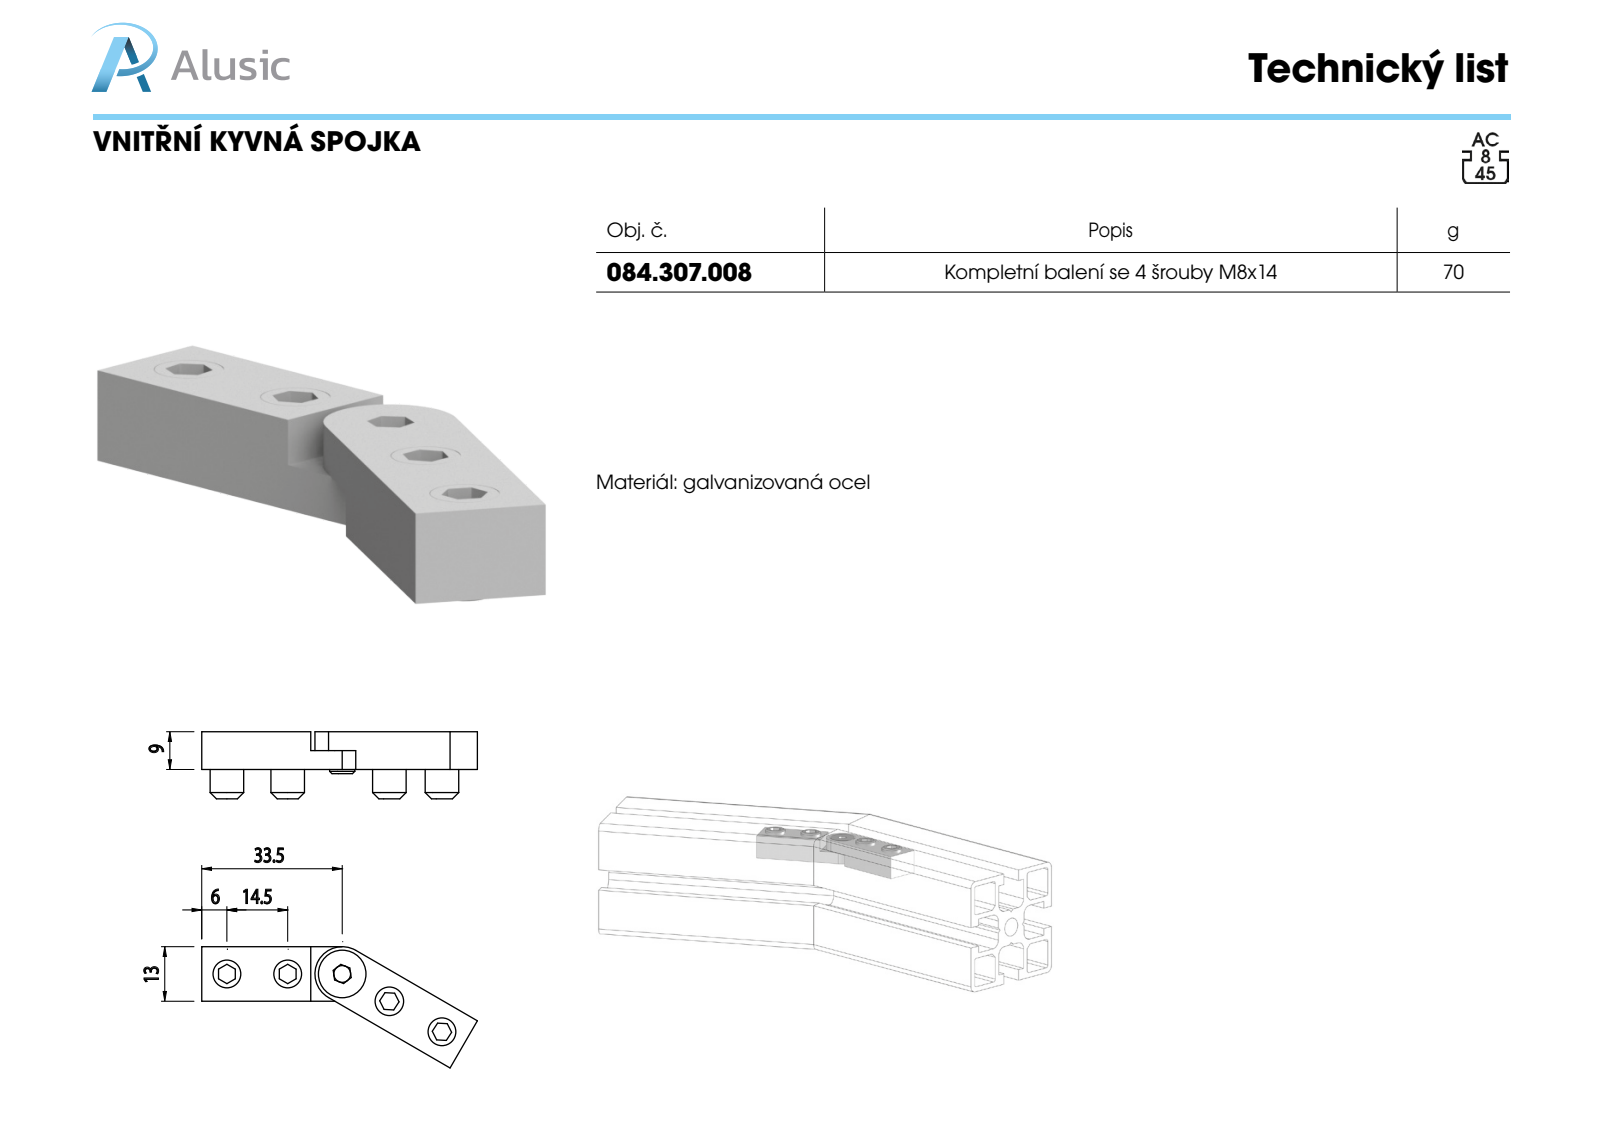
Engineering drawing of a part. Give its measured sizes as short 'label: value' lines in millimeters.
name: 084.307.008A; socket set screw cone point_iso_ISO 4027 - M8 x 6-N; socket countersunk head screw_iso_PreviewCfg; 084.307.008B (+1 more)
written by: SolidWorks 2011 (CONFIG_CONTROL_DESIGN)
unit: mm
bodies: 7 solids, 114 faces (60 planar, 28 cylindrical, 26 other)
size: 65.76 × 28.88 × 11.5
volume: 6 870 mm³; area: 5 301 mm²
holes: 4× ⌀6.8, 1× ⌀5, 1× ⌀5.5
bosses: 4× ⌀8, 1× ⌀13, 1× ⌀7.53, 1× ⌀4
face distances: 9, 4.5, 13, 1.5, 26, 3, 10.5, 6, 4, 7.5
hole spacings: 13, 14.5, 27.5, 39.3, 25.12, 53.13
